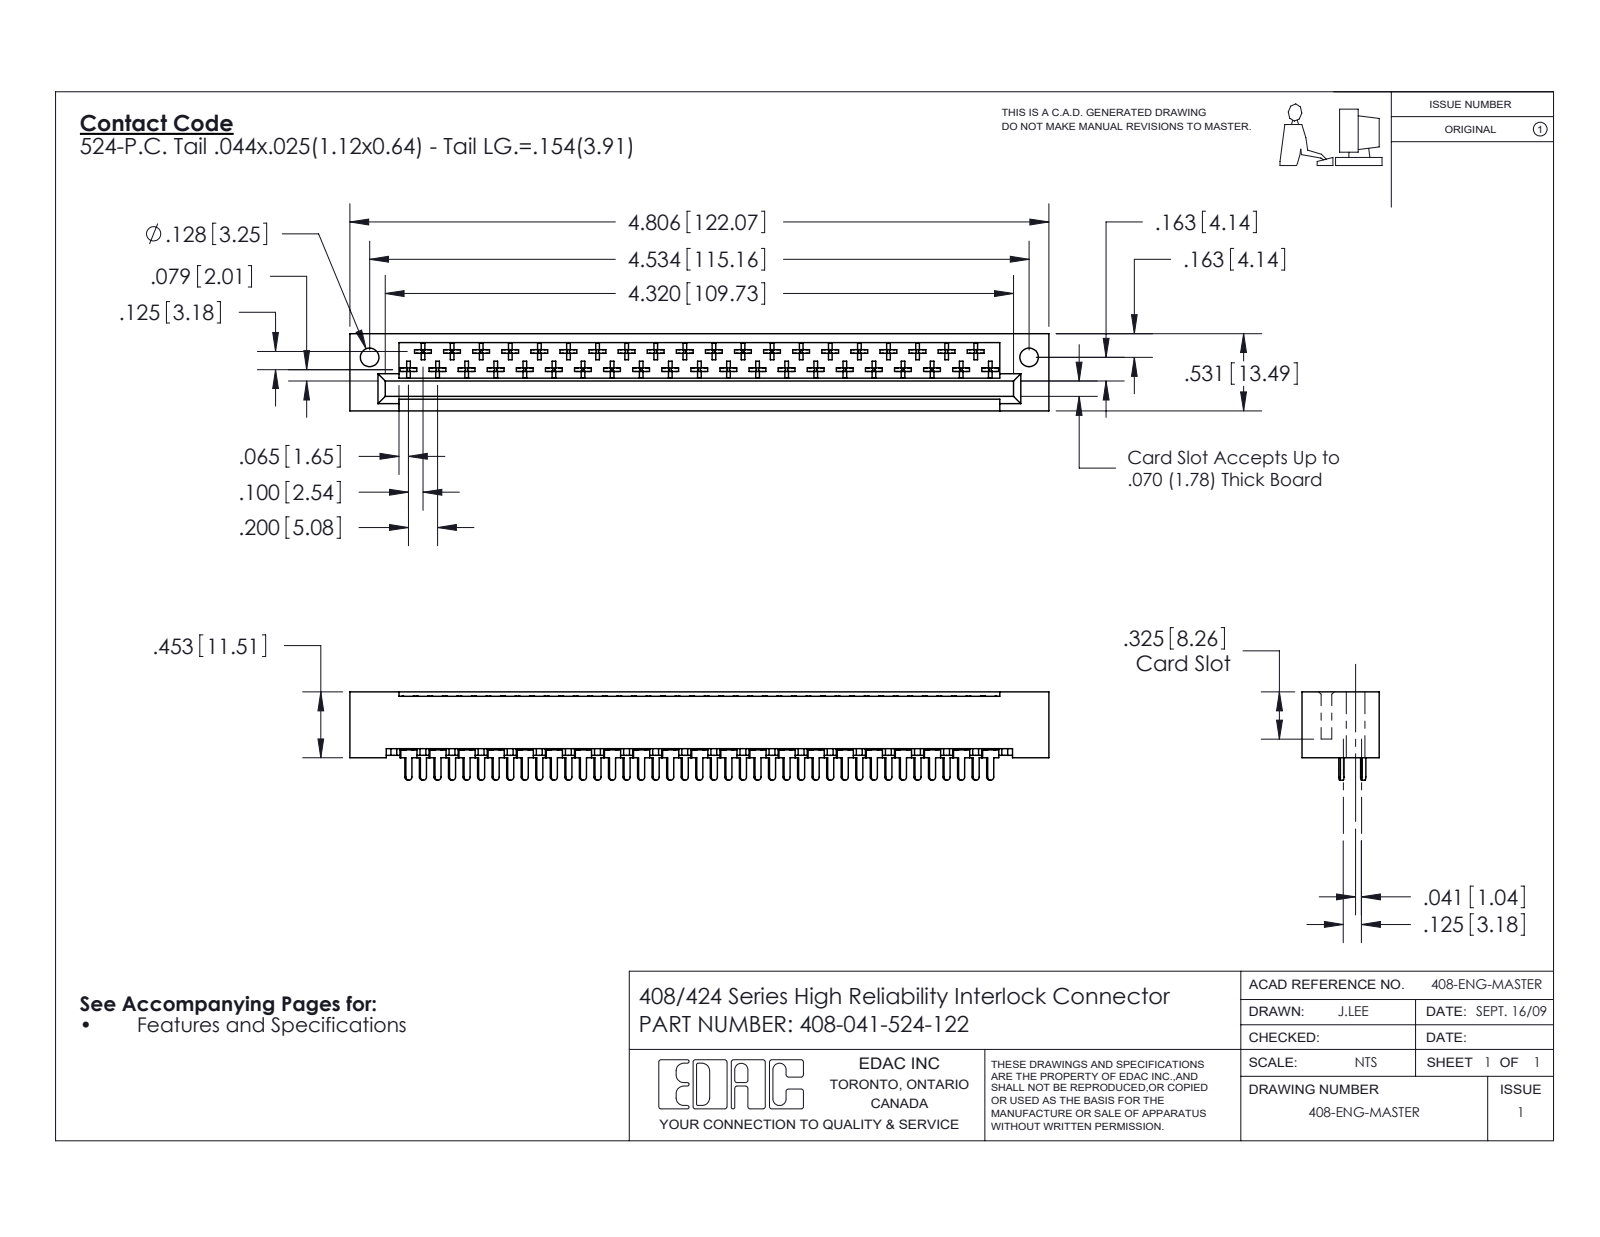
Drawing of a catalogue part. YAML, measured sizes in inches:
part_name: "408 Part_041 - 1; 408-047-524-122; 408-290-001_408-290-124 - Top; 408-290-001_408-290-124 - Bottom"
step_written_by: "SolidWorks 2016 (CONFIG_CONTROL_DESIGN)"
units: inches
bodies: {solids: 42, faces: 2299, planar: 1758, cylindrical: 377, other: 164}
overall_size: [4.806, 0.607, 0.531]
volume: 0.811
surface_area: 25.94
round_holes:
  - {diameter: 0.128, count: 2}
partial_cylinders:
  - {radius: 0.01, count: 246}
  - {radius: 0.02, count: 43}
  - {radius: 0.022, count: 41}
face_to_face_distances: [0.1, 0.296, 0.531, 0.125, 0.025, 0.025, 0.259, 0.272, 0.235, 0.135]
hole_center_spacings: [4.534]
